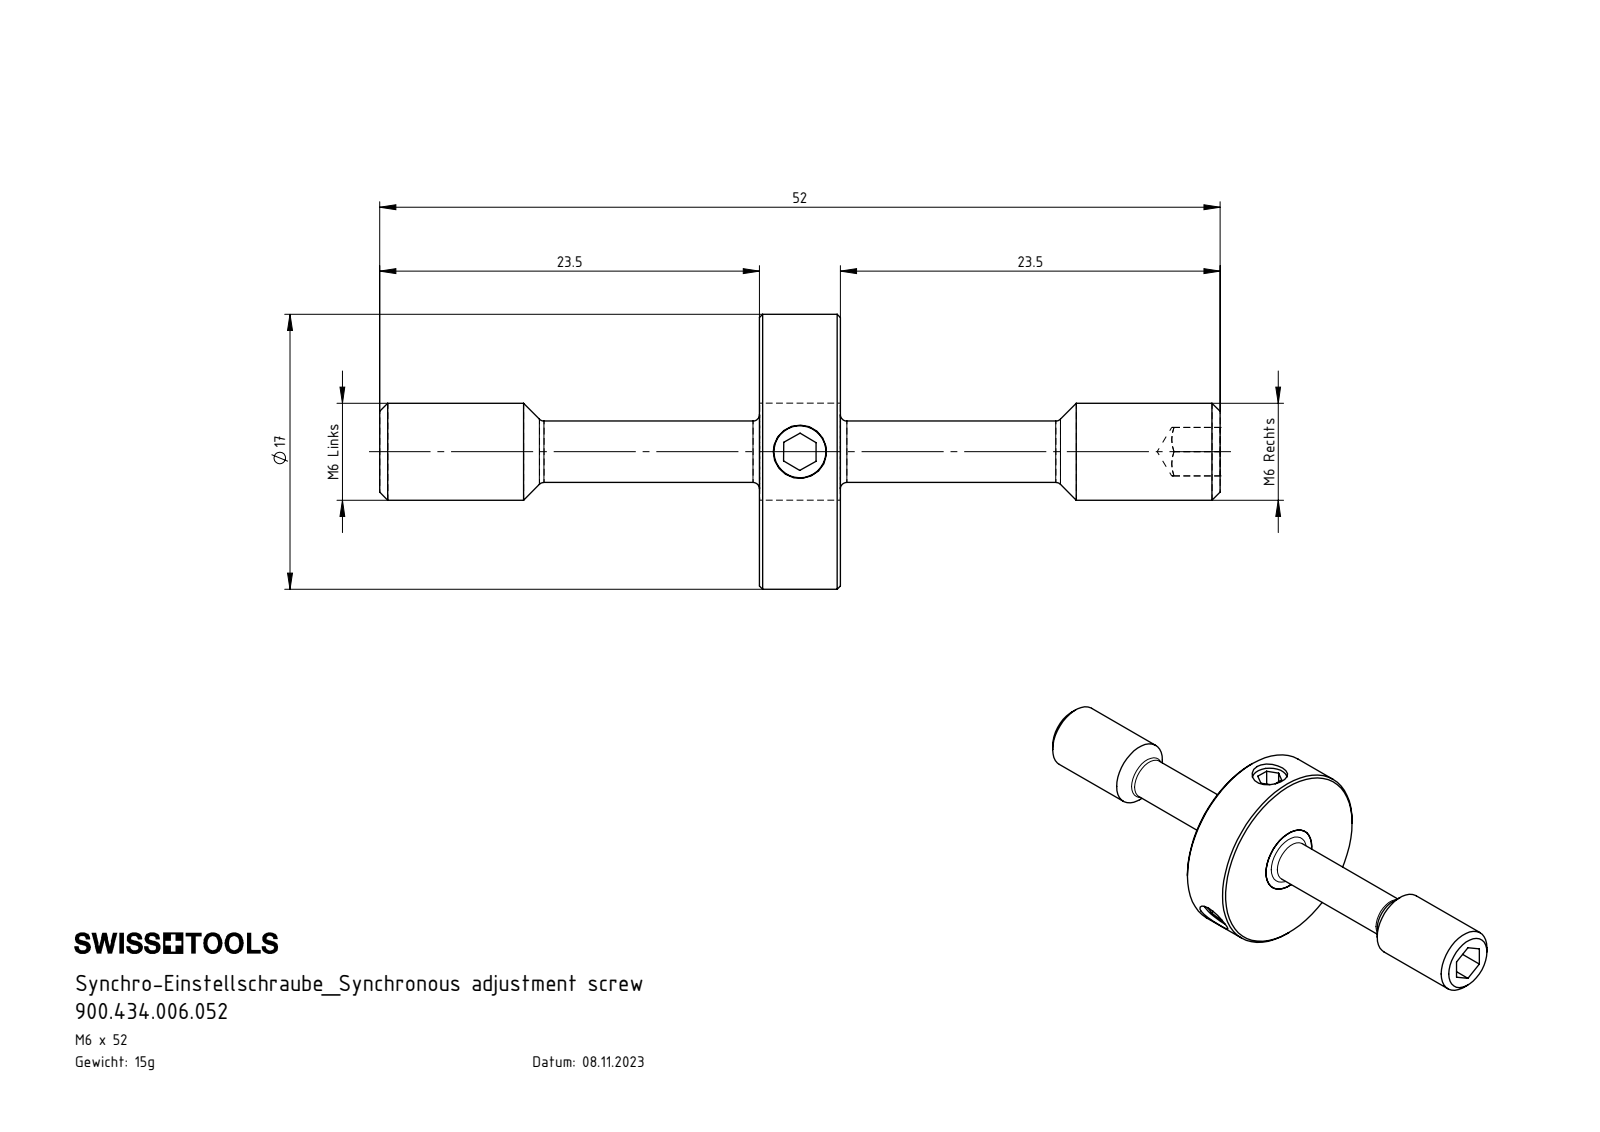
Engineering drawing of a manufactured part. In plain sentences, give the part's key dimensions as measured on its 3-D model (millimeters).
The part is named "ISO 4026 - M4 x 5; 900.434.006.052; Z42-ER3.002.005_A; Z55-ER3.001.052_A". Its 3-D file was written by "SolidWorks 2022 (AUTOMOTIVE_DESIGN)". It is 5 solids with 99 faces: 39 planar, 26 cylindrical and 34 other. Overall it measures 52 by 17 by 17 millimeters. Its volume is 1 964 cubic millimeters and its surface area 2 067 square millimeters. Round holes: 3 of diameter 3.3. Round bosses or shafts: 3 of diameter 4, 1 of diameter 17, 1 of diameter 6, 1 of diameter 3.8. The main face-to-face distances are 5, 23.5, 28.5, 2, 2.5, 3, 52, 25, 27, 1.5.
